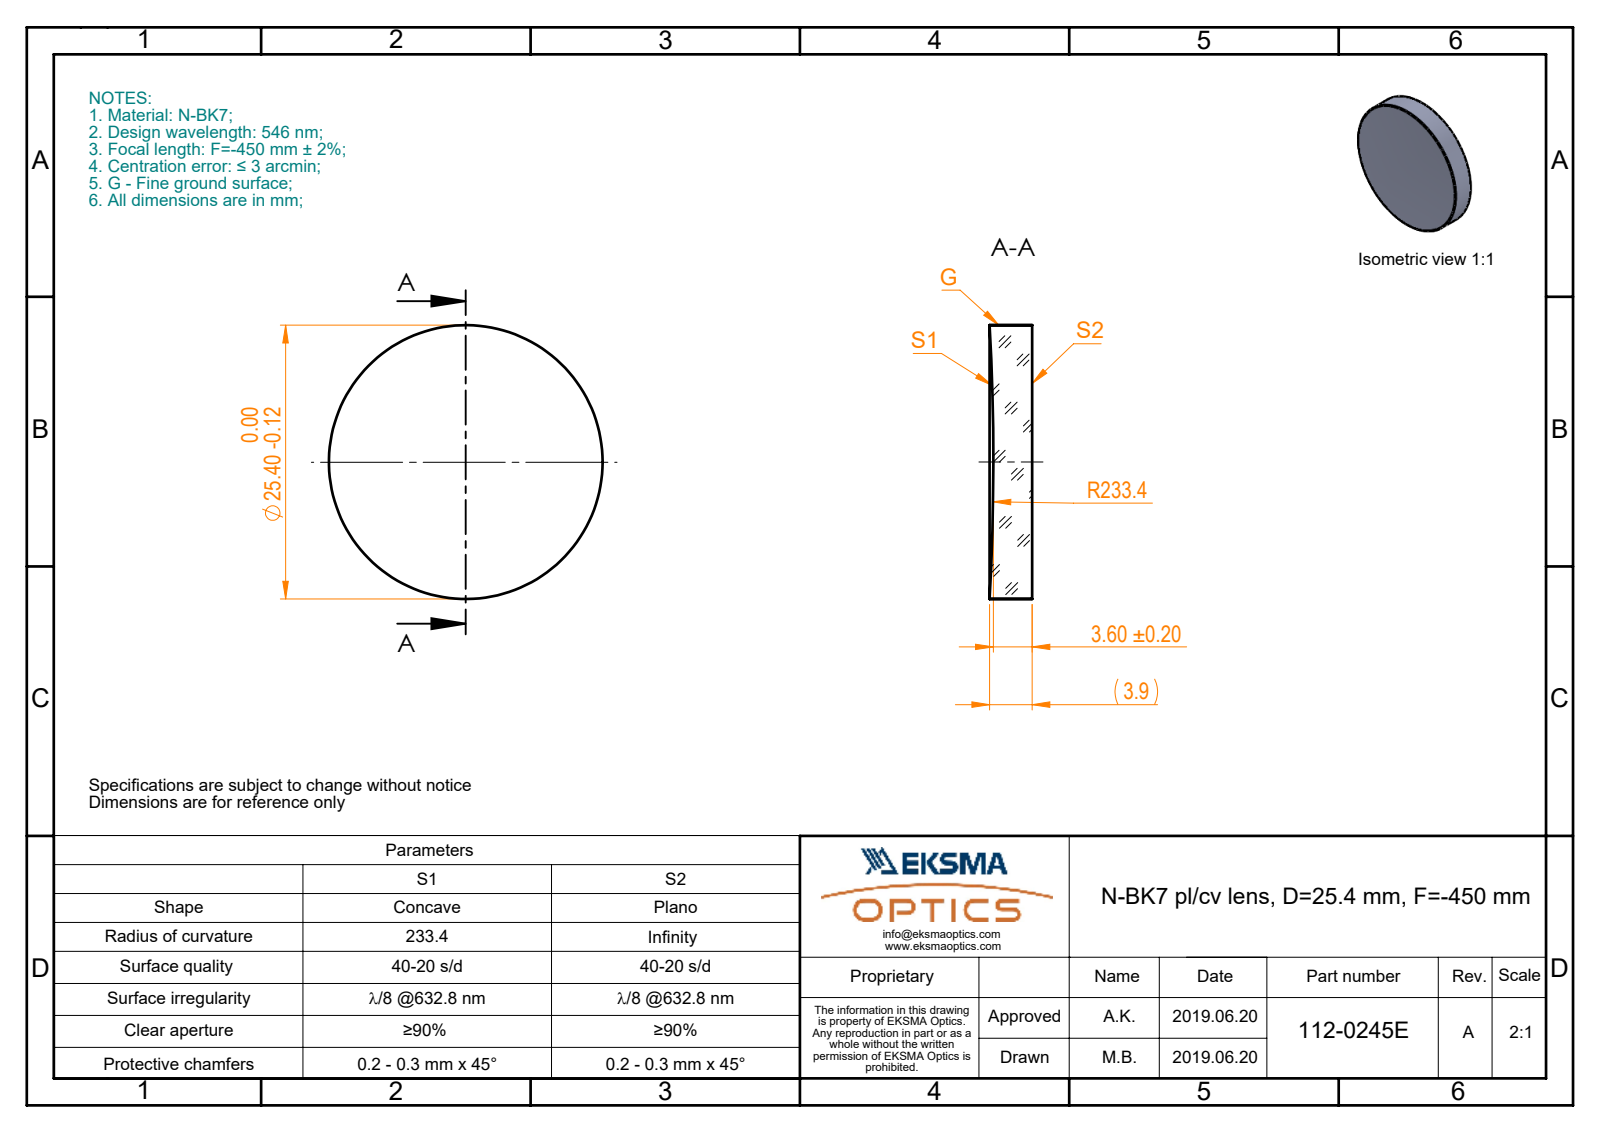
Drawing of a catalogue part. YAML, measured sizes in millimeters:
part_name: "112-0245E BK7 pl-cv 25.4 F-450"
step_written_by: "SolidWorks 2017 (CONFIG_CONTROL_DESIGN)"
units: millimeters
bodies: {solids: 1, faces: 5, planar: 1, cylindrical: 2, other: 2}
overall_size: [25.4, 25.4, 3.95]
volume: 1912
surface_area: 1329
round_bosses_or_shafts:
  - {diameter: 25.4, count: 1}
